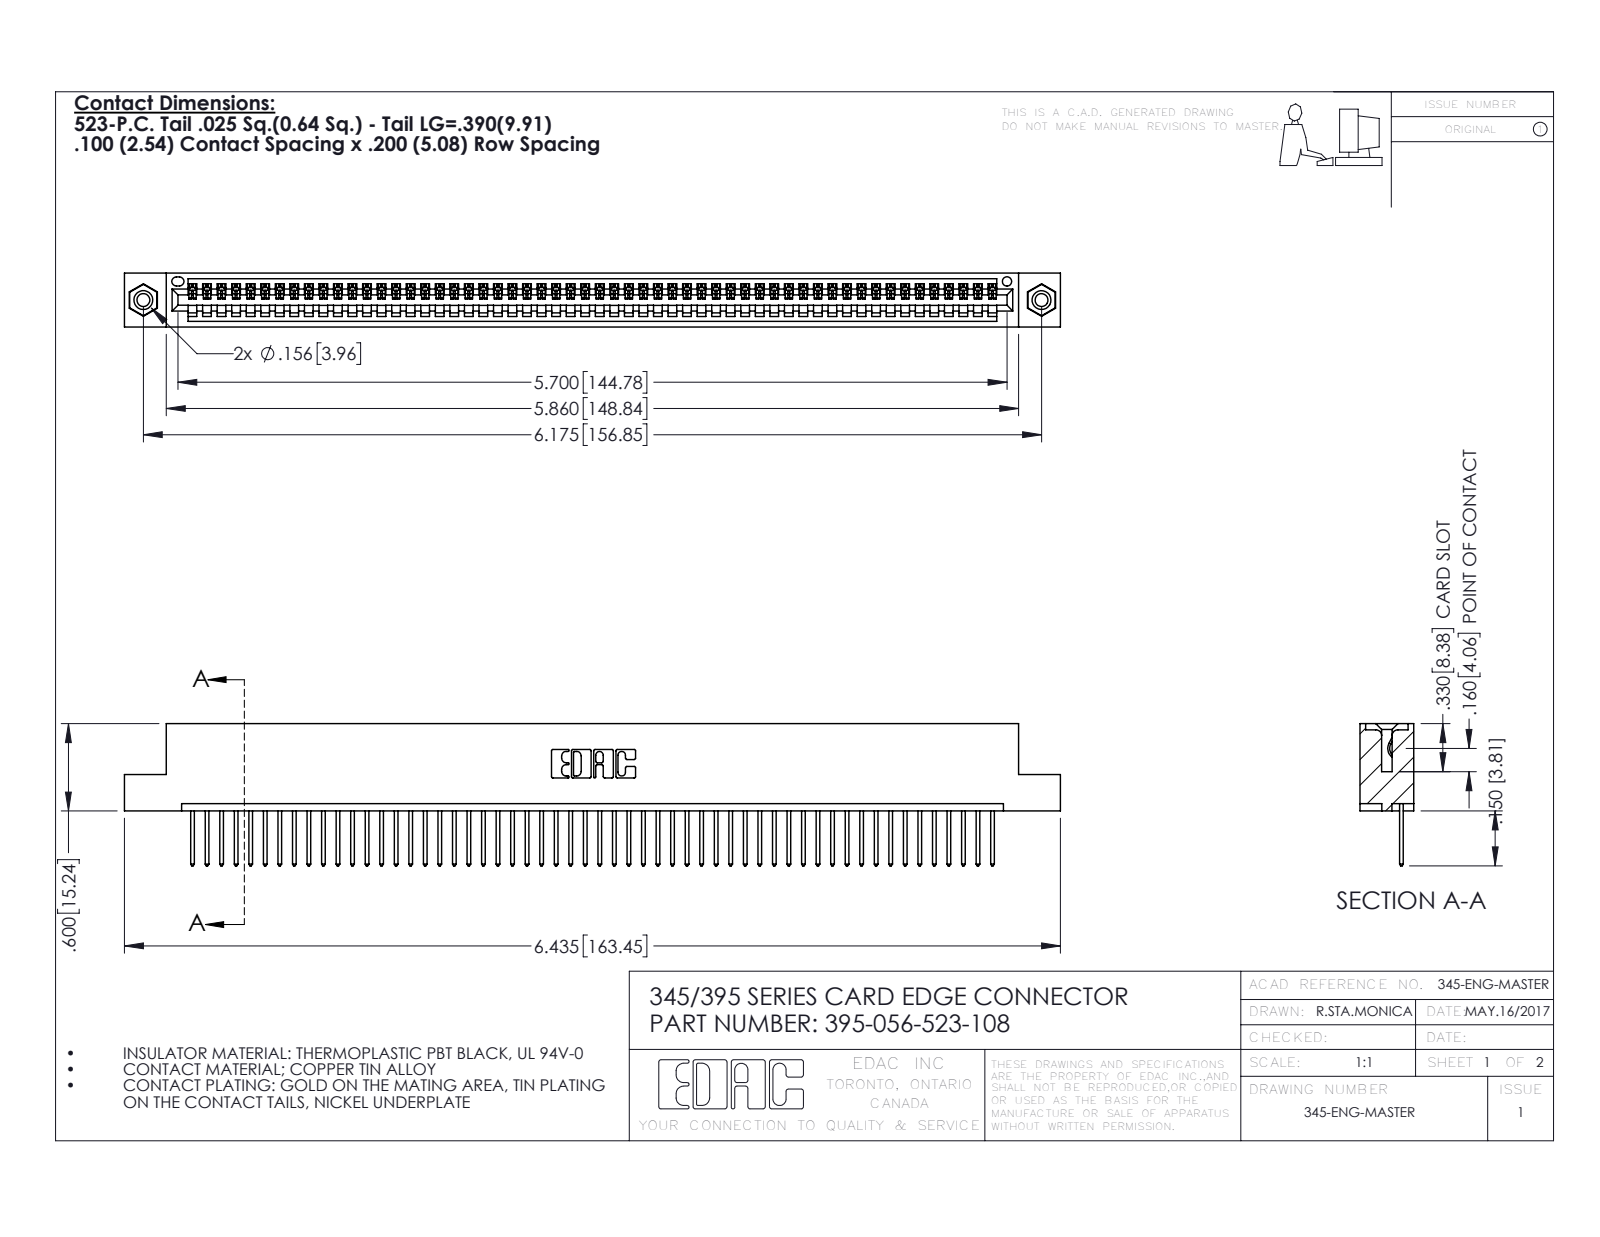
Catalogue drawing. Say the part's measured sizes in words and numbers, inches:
The part is named "395-056-523-108; 345-250-001_345-250-003-102; 345 Part_Flush Mounting Lugs - 0.156 Dia-TI; 345-292-001_345-293-123". Its 3-D file was written by "SolidWorks 2016 (CONFIG_CONTROL_DESIGN)". It is 59 solids with 3434 faces: 2352 planar, 1066 cylindrical and 16 other. Overall it measures 6.435 by 0.977 by 0.37 inches. Its volume is 0.953 cubic inches and its surface area 32.58 square inches. Round holes: 2 of diameter 0.089, 2 of diameter 0.125, 2 of diameter 0.156, 1 of diameter 0.064. Round bosses or shafts: 2 of diameter 0.155. Partial cylindrical surfaces (rounded edges, fillets, slot ends): 112 of radius 0.006, 112 of radius 0.01, 22 of radius 0.01, 6 of radius 0.007, 6 of radius 0.031, 3 of radius 0.026, 2 of radius 0.031, 2 of radius 0.04. The main face-to-face distances are 0.072, 0.298, 0.37, 0.2, 0.098, 0.272, 0.025, 0.225, 0.149, 0.072. The hole center spacings are 0.27, 5.939, 6.175.
